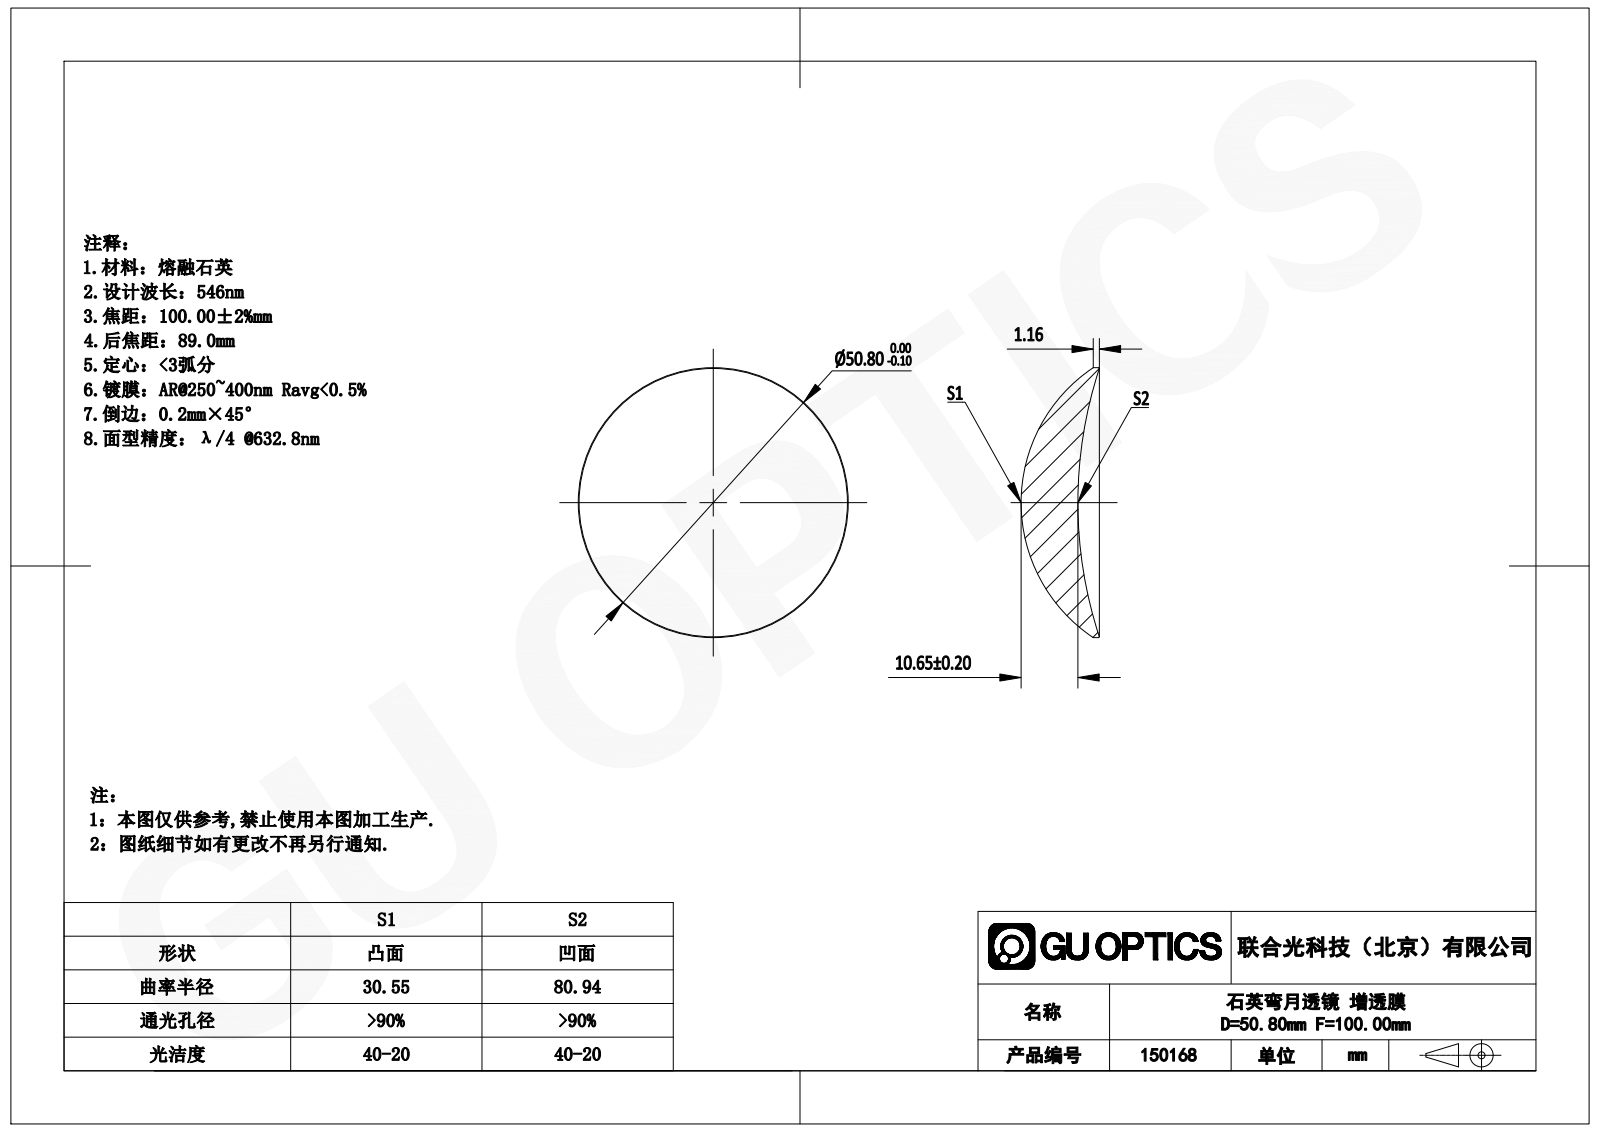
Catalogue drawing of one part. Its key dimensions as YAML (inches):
part_name: "GLM2-050B-100-UV"
step_written_by: "SolidWorks 2022 (AUTOMOTIVE_DESIGN)"
units: inches
bodies: {solids: 1, faces: 8, planar: 0, cylindrical: 2, other: 6}
overall_size: [2, 2, 0.58]
volume: 0.813
surface_area: 7.522
round_bosses_or_shafts:
  - {diameter: 2, count: 1}
